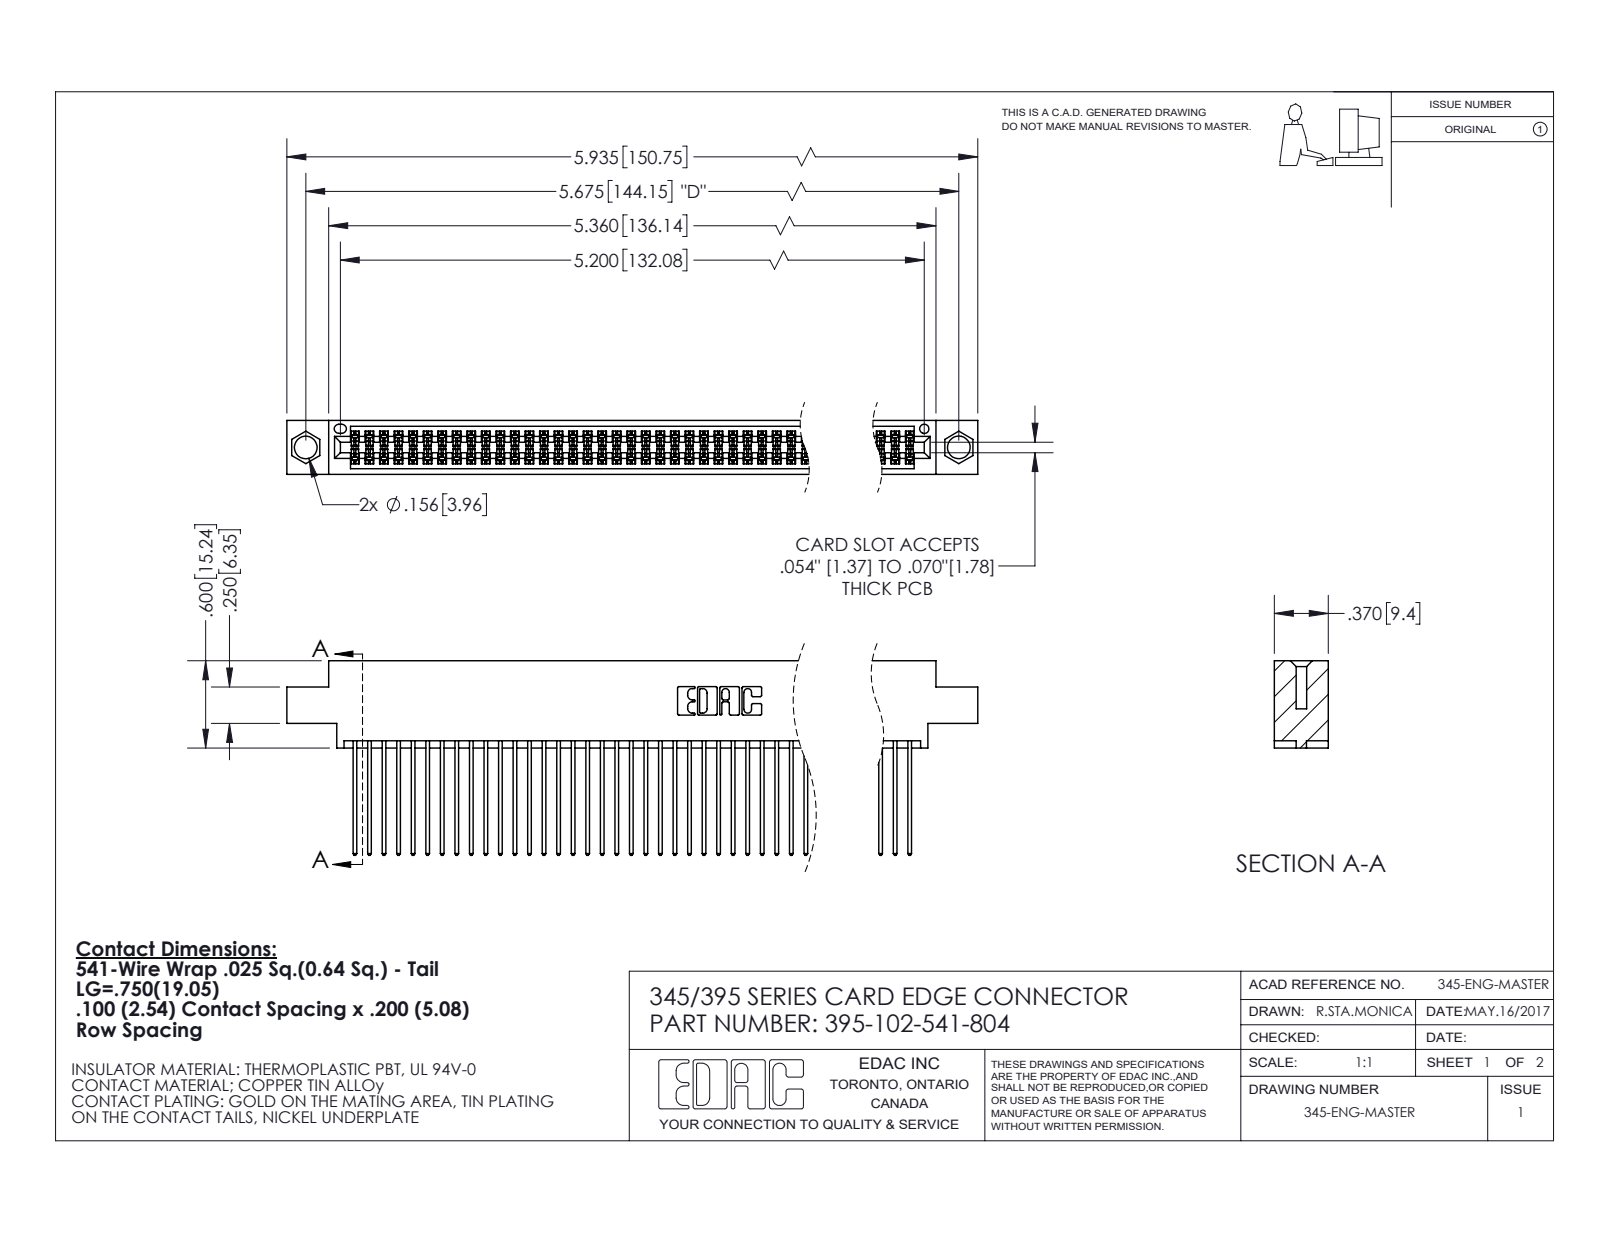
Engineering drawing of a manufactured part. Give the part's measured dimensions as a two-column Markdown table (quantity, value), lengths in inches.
| quantity | value |
| --- | --- |
| part name | 345 Part_0.170 Offset - 0.156 Dia-TI; 345-292-001_345-293-141; 395-102-541-804 |
| STEP written by | SolidWorks 2020 (CONFIG_CONTROL_DESIGN) |
| units | inches |
| bodies | 103 solids, 5244 faces (3464 planar, 1780 cylindrical, 0 other) |
| overall size | 5.935 × 1.337 × 0.37 |
| volume | 0.921 in³ |
| surface area | 39.11 in² |
| round holes (diameter × count) | 0.156 × 2, 0.064 × 1 |
| partial cylindrical surfaces (radius × count) | 0.006 × 153, 0.01 × 102, 0.01 × 22, 0.007 × 6, 0.031 × 6, 0.026 × 3, 0.014 × 2, 0.019 × 2 |
| main face-to-face distances | 0.072, 0.298, 0.2, 0.098, 0.272, 0.025, 0.225, 0.37, 0.175, 0.149 |
| hole center spacings | 0.27, 5.439, 5.675 |
